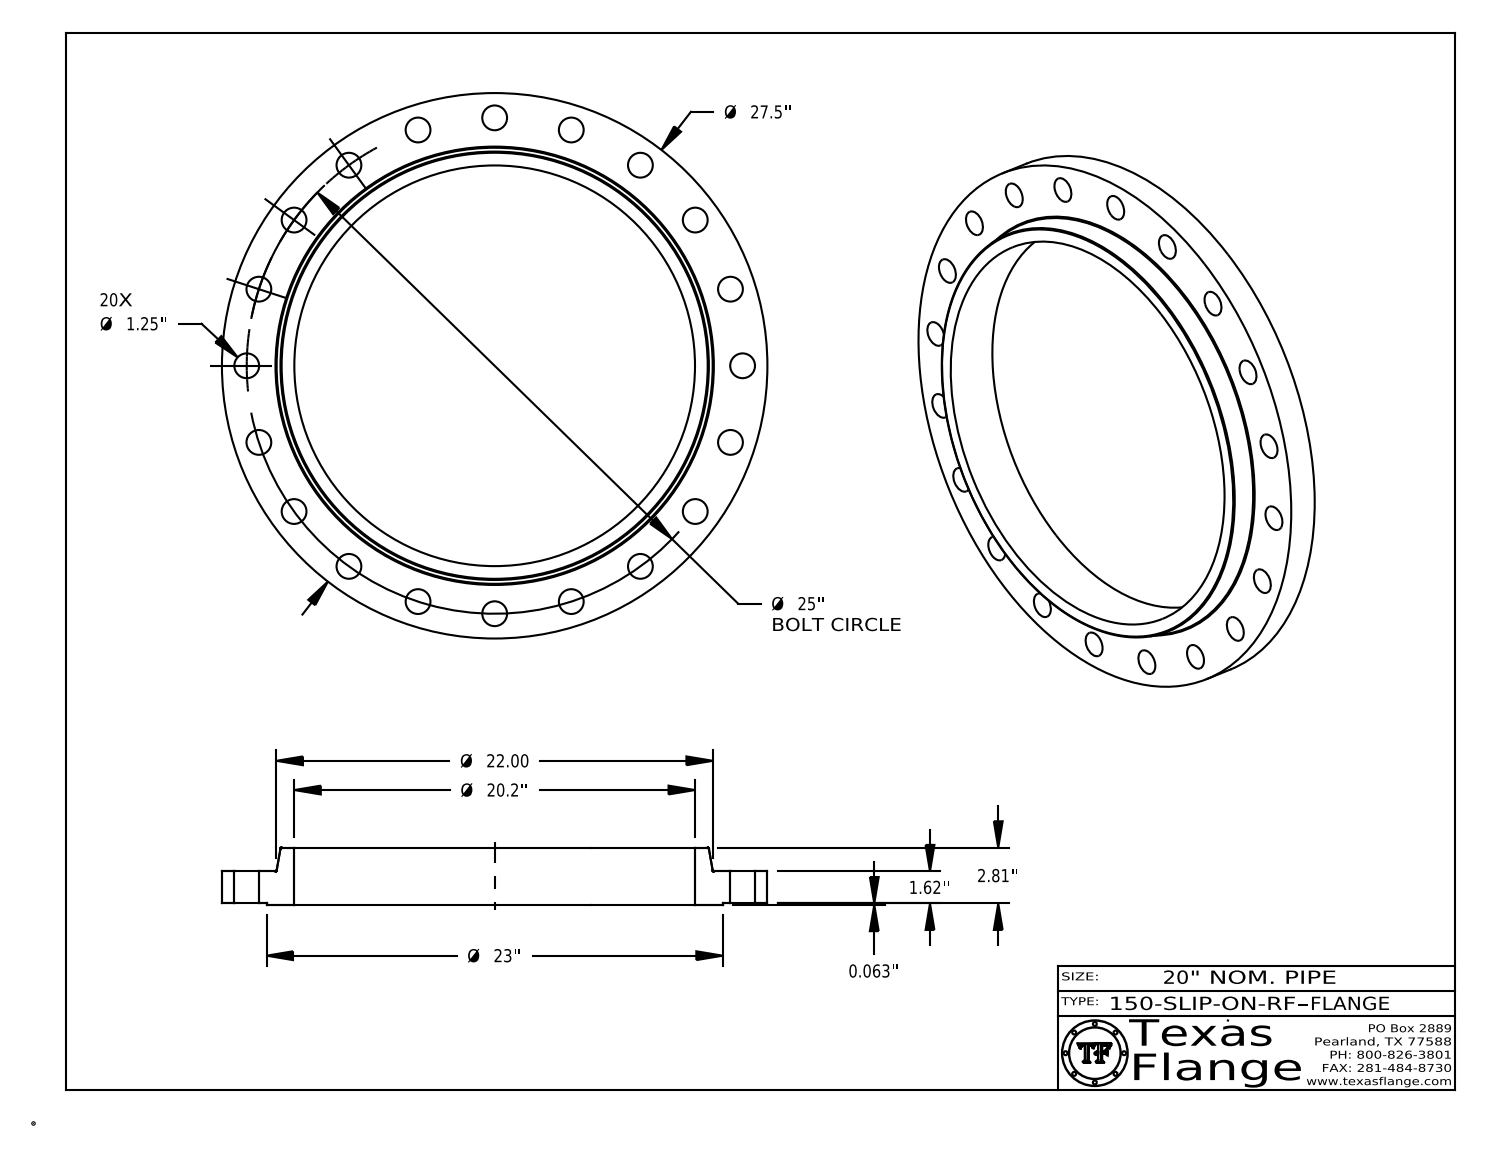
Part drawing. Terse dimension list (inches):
name: 150-SLIP-ON-RF
written by: CATIA V5 STEP AP214 (AUTOMOTIVE_DESIGN)
unit: in
bodies: 1 solid, 441 faces (369 planar, 66 cylindrical, 6 other)
size: 27.5 × 27.5 × 2.873
volume: 471.6 in³; area: 1 018 in²
holes: 20× ⌀1.25, 1× ⌀0.495, 1× ⌀20.2
bosses: 8× ⌀0.03, 1× ⌀27.5, 1× ⌀23, 1× ⌀0.39
face distances: 1.62, 0.063, 1.683, 2.872, 2.81, 1.19, 1.668, 1.605, 0.015, 1.205
hole spacings: 12.5, 14.694, 17.678, 20.225, 23.776, 24.692, 11.35, 22.275
